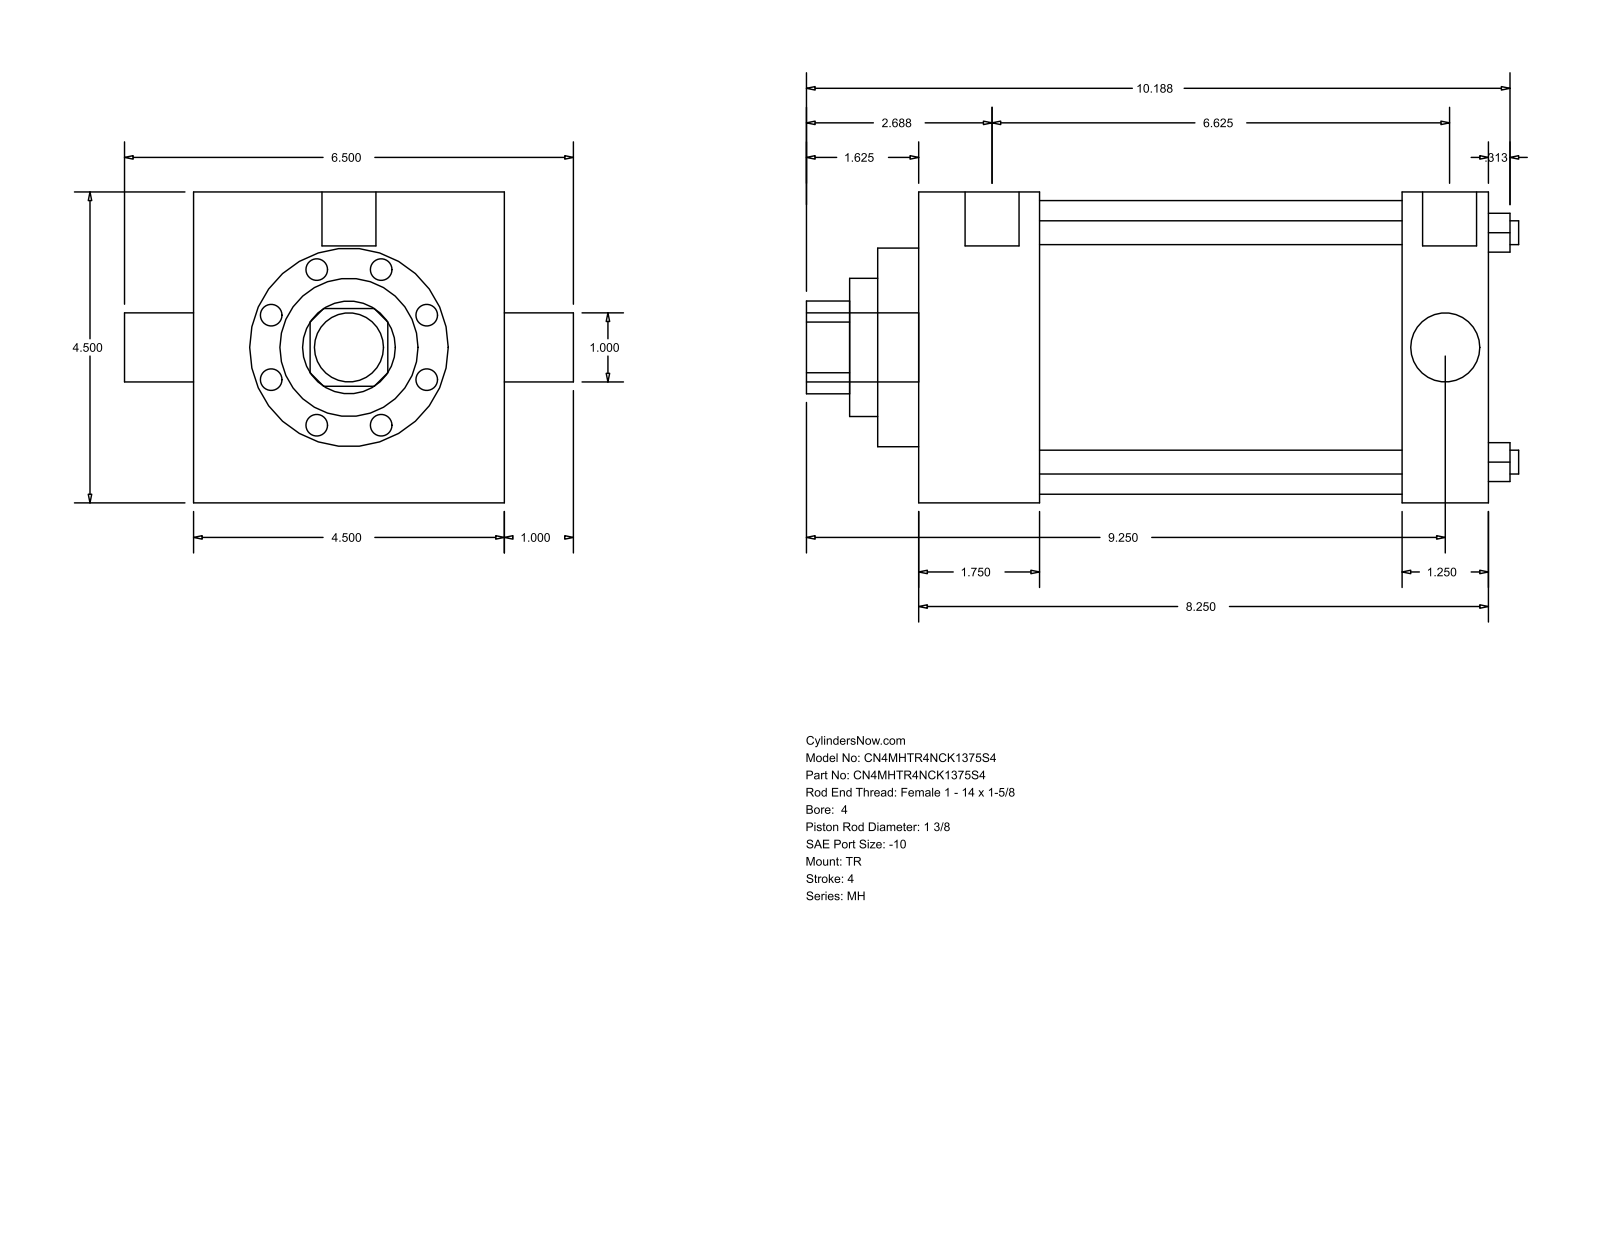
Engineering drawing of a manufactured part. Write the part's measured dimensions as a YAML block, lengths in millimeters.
part_name: "MH_TR__0400_1.375"
step_written_by: "GSSL Pune (CONFIG_CONTROL_DESIGN)"
units: millimeters
bodies: {solids: 0, faces: 86, planar: 61, cylindrical: 25, other: 0}
overall_size: [261.94, 165.1, 114.3]
round_holes:
  - {diameter: 8.76, count: 4}
  - {diameter: 25.4, count: 1}
  - {diameter: 34.92, count: 1}
  - {diameter: 50.8, count: 1}
  - {diameter: 73.03, count: 1}
  - {diameter: 107.95, count: 1}
round_bosses_or_shafts:
  - {diameter: 8.73, count: 3}
  - {diameter: 19.84, count: 2}
  - {diameter: 25.4, count: 1}
partial_cylinders:
  - {radius: 17.06, count: 1}
face_to_face_distances: [114.3, 209.55, 165.1, 44.45, 177.8, 133.35, 31.75, 15.08, 59.53, 192.88]
hole_center_spacings: [59.62, 84.32, 119.25]
